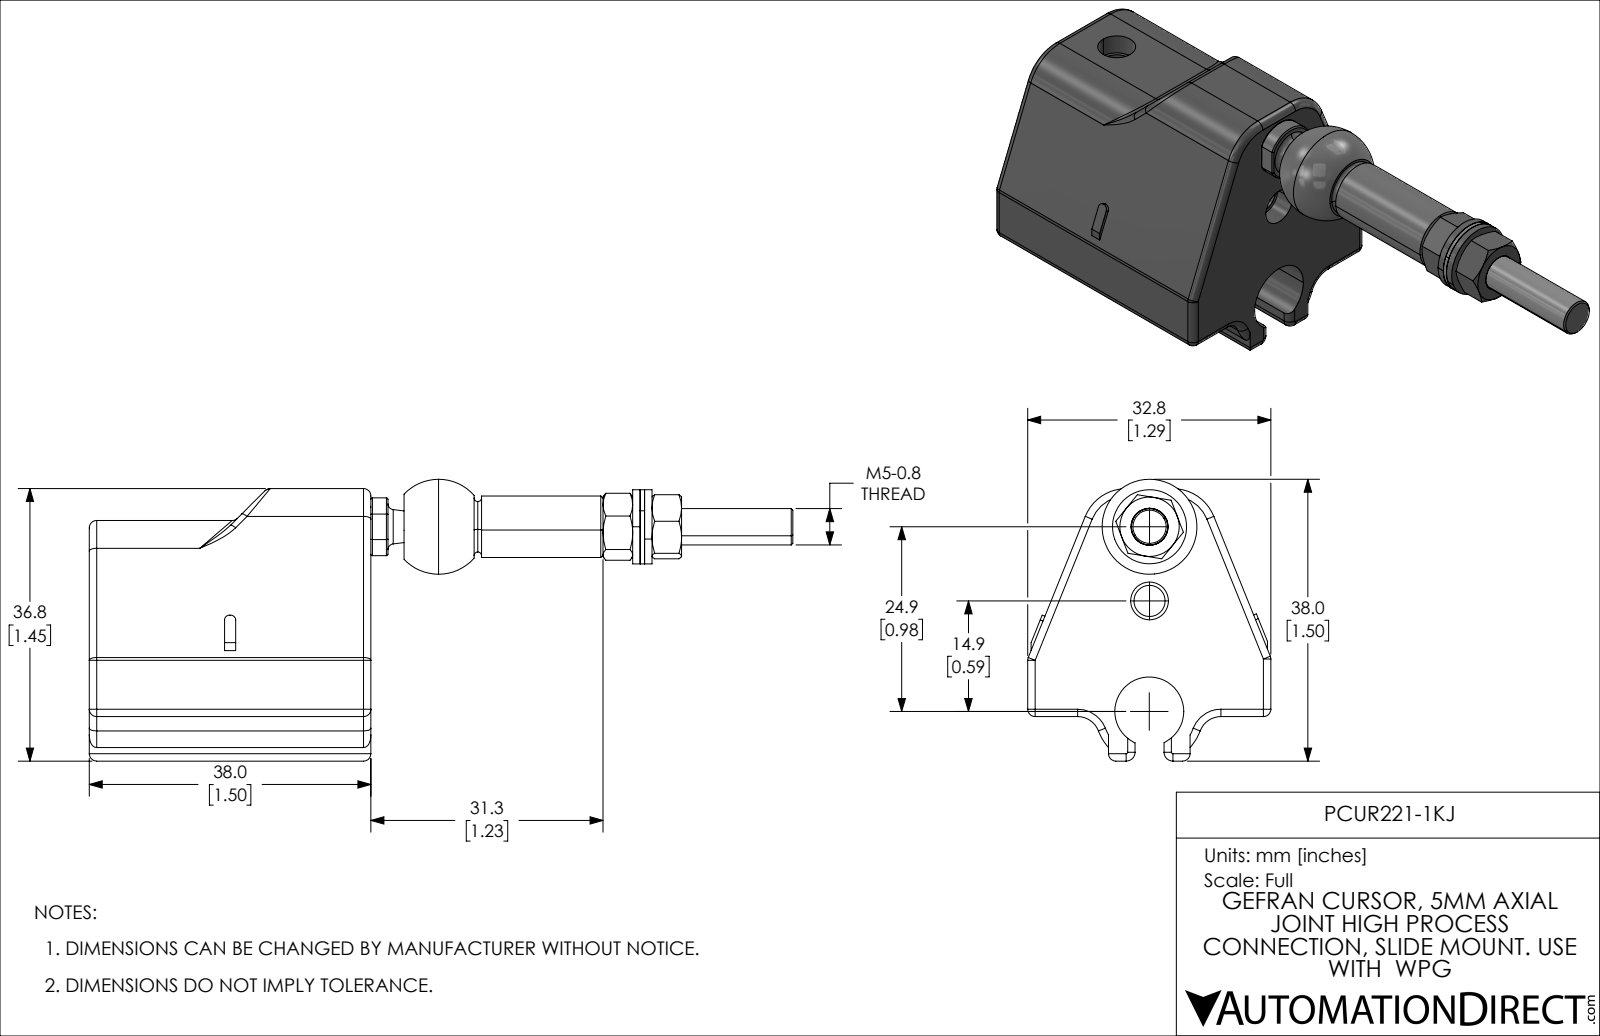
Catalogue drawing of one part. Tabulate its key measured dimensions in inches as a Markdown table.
| quantity | value |
| --- | --- |
| part name | PCUR221-1KJ |
| STEP written by | SolidWorks 2021 (CONFIG_CONTROL_DESIGN) |
| units | inches |
| bodies | 9 solids, 367 faces (90 planar, 129 cylindrical, 148 other) |
| overall size | 3.737 × 1.496 × 1.291 |
| volume | 1.803 in³ |
| surface area | 17.71 in² |
| round holes (diameter × count) | 0.165 × 3, 0.201 × 3, 0.197 × 1, 0.209 × 1, 0.366 × 1 |
| round bosses / shafts (diameter × count) | 0.394 × 1, 0.327 × 1, 0.193 × 1 |
| partial cylindrical surfaces (radius × count) | 0.039 × 28, 0.018 × 8, 0.008 × 4, 0.028 × 4, 0.236 × 4, 0.047 × 2, 0.118 × 2, 0.154 × 1 |
| main face-to-face distances | 1.496, 0.472, 0.512, 0.882, 0.409, 0.984, 1.291, 0.039, 1.041, 0.063 |
| hole center spacings | 0.394, 0.587, 0.98 |
